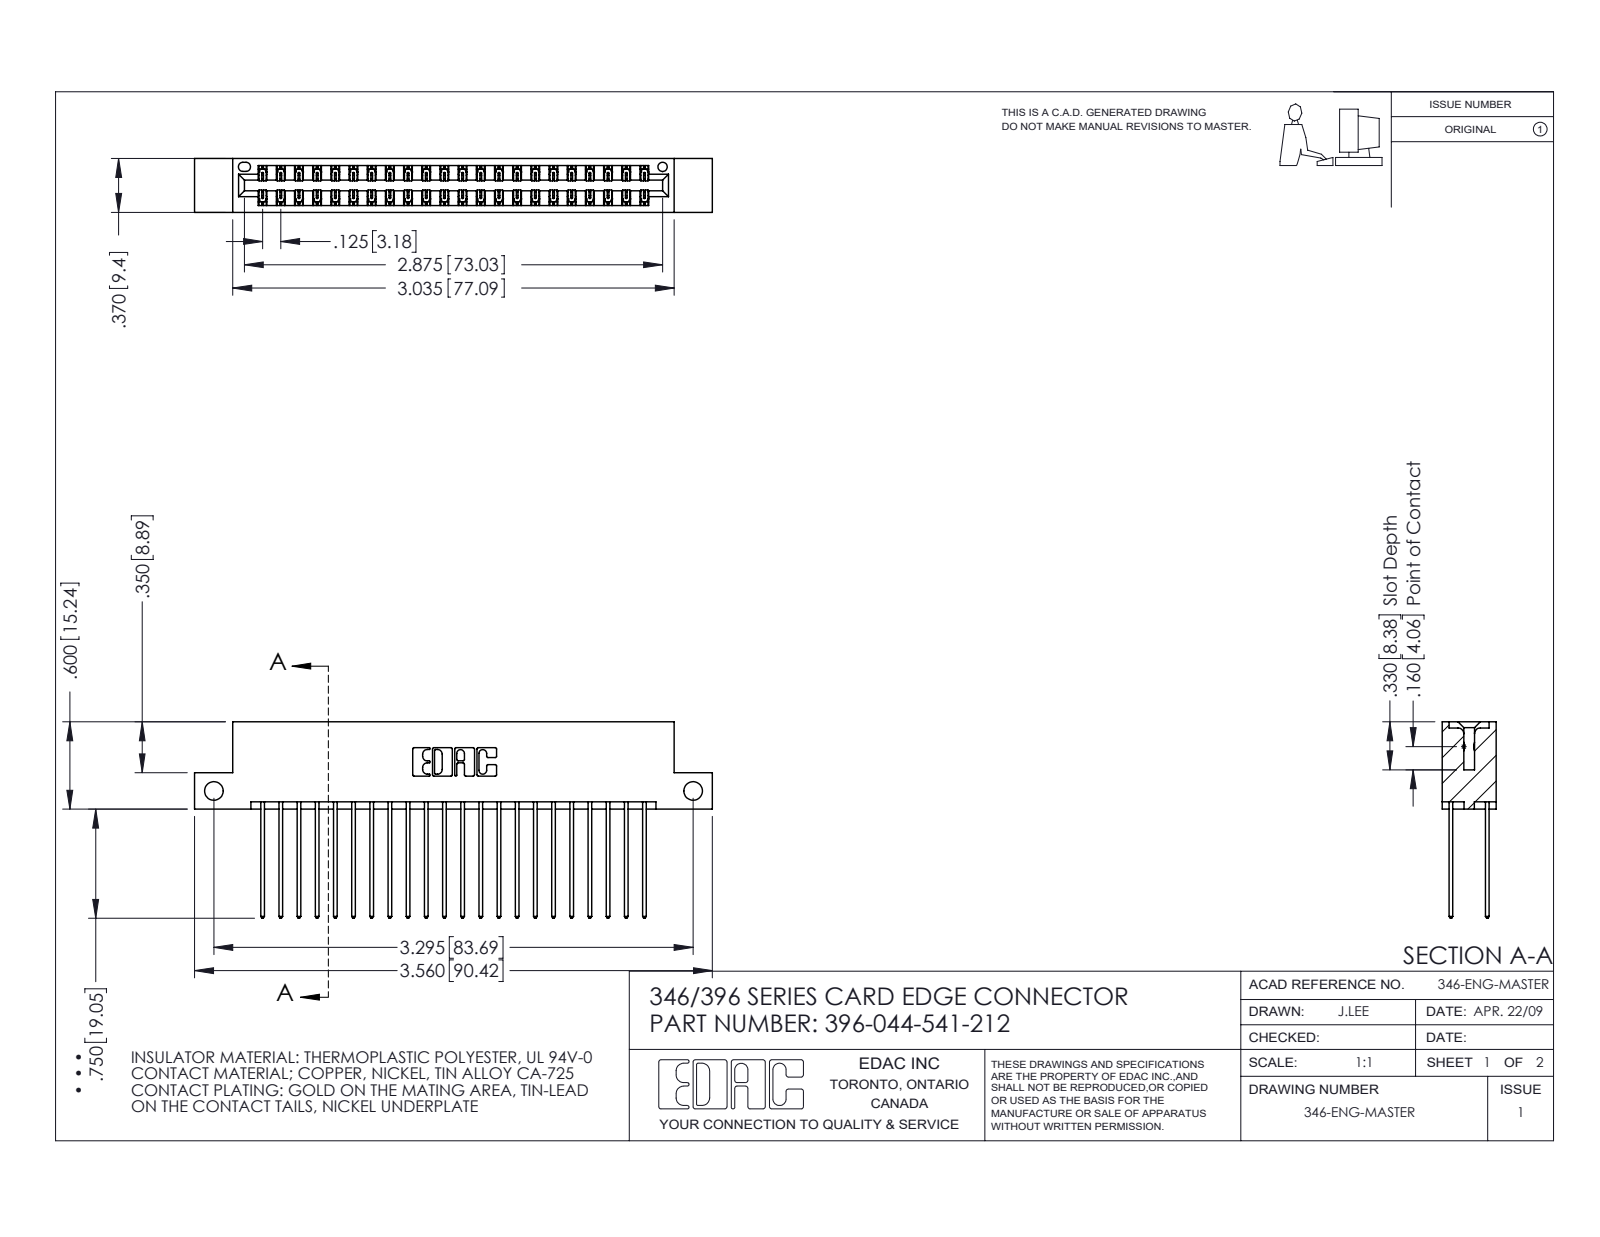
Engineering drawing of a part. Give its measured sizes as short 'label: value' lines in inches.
name: 396-044-541-212; 345-292-001_345-293-141; 346 Part_Flush Mounting Lugs - Side Mount
written by: SolidWorks 2016 (CONFIG_CONTROL_DESIGN)
unit: in
bodies: 45 solids, 2410 faces (1616 planar, 794 cylindrical, 0 other)
size: 3.56 × 1.35 × 0.37
volume: 0.539 in³; area: 19.98 in²
holes: 2× ⌀0.128, 1× ⌀0.064
rounds: 66× R0.006, 44× R0.01, 22× R0.01, 6× R0.007, 6× R0.031, 3× R0.026, 2× R0.014, 2× R0.022
face distances: 0.048, 0.322, 0.25, 0.072, 0.298, 0.025, 0.37, 0.275, 0.148, 0.222
hole spacings: 3.295
